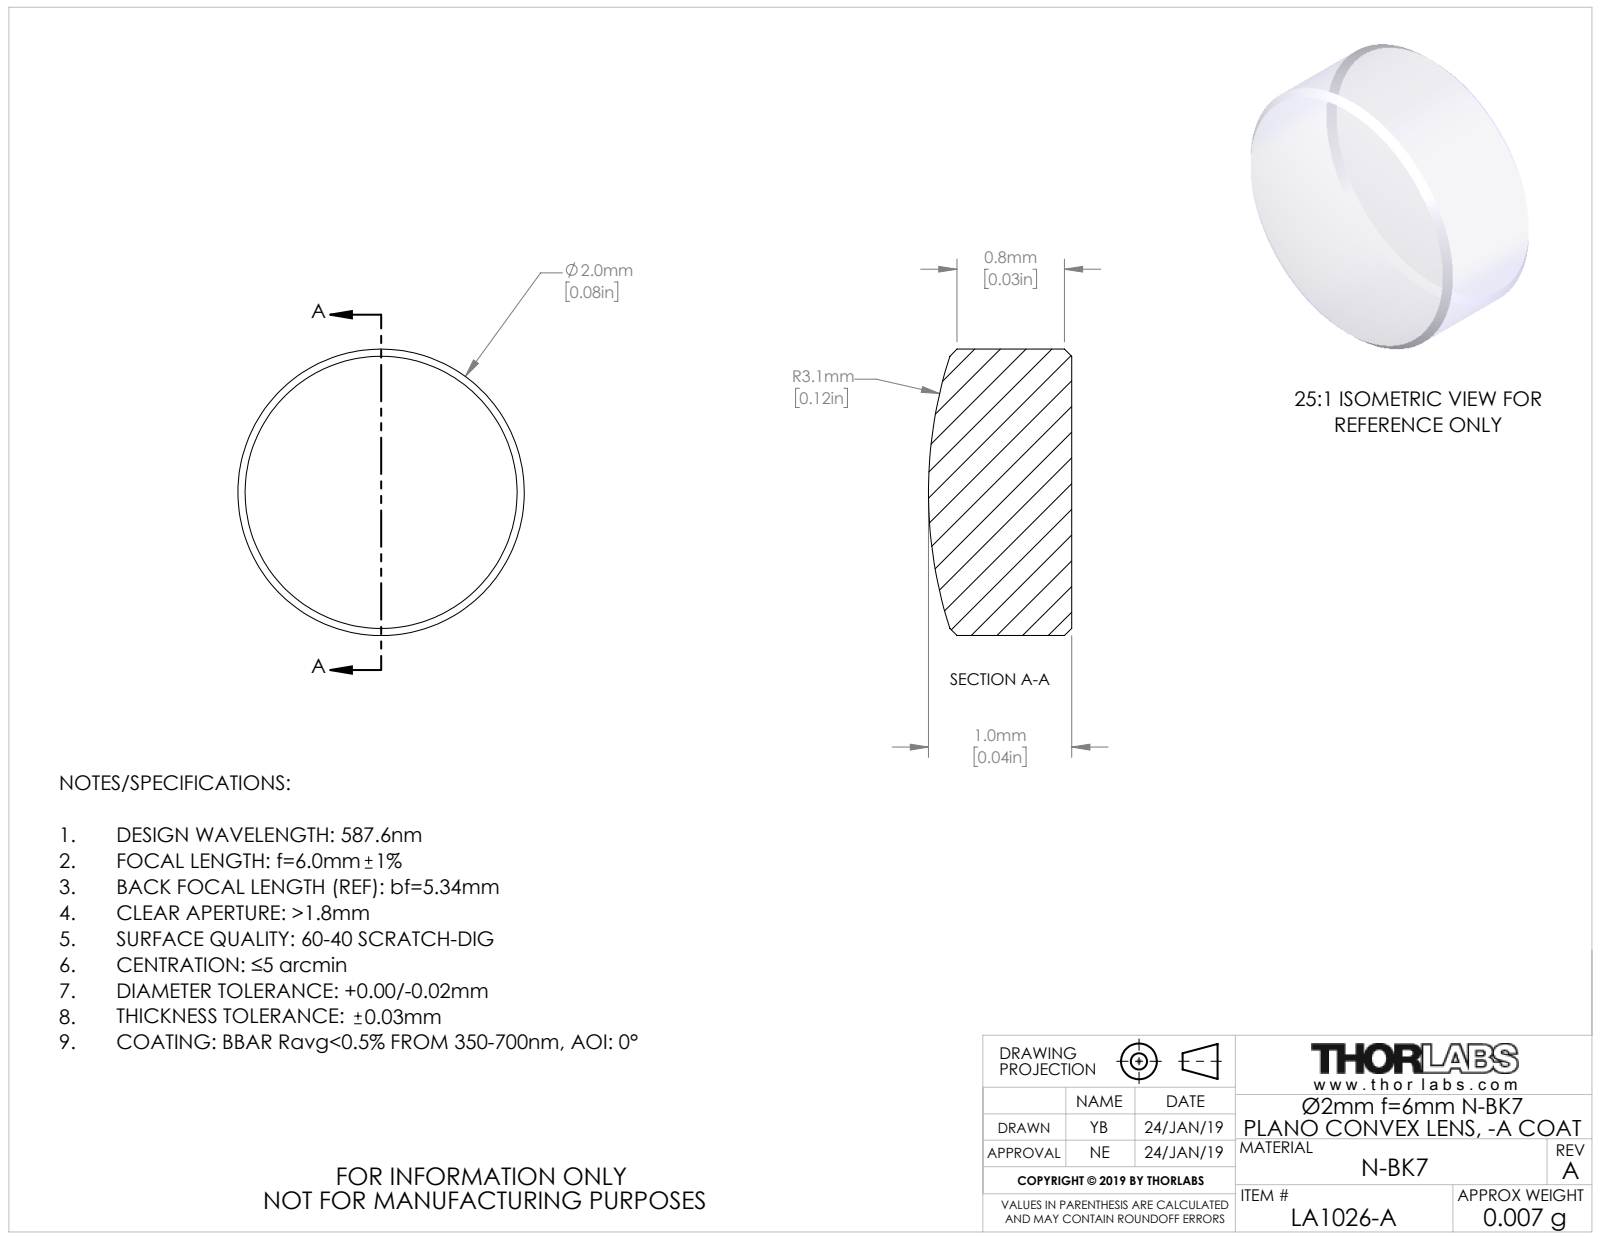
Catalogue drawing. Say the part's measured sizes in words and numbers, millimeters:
The part is named "TTN182809-E0W". Its 3-D file was written by "SolidWorks 2018 (CONFIG_CONTROL_DESIGN)". It is 1 solid with 9 faces: 1 planar, 2 cylindrical and 6 other. Overall it measures 2 by 2 by 1 millimeters. Its volume is 3 cubic millimeters and its surface area 11 square millimeters. Round bosses or shafts: 1 of diameter 2.
